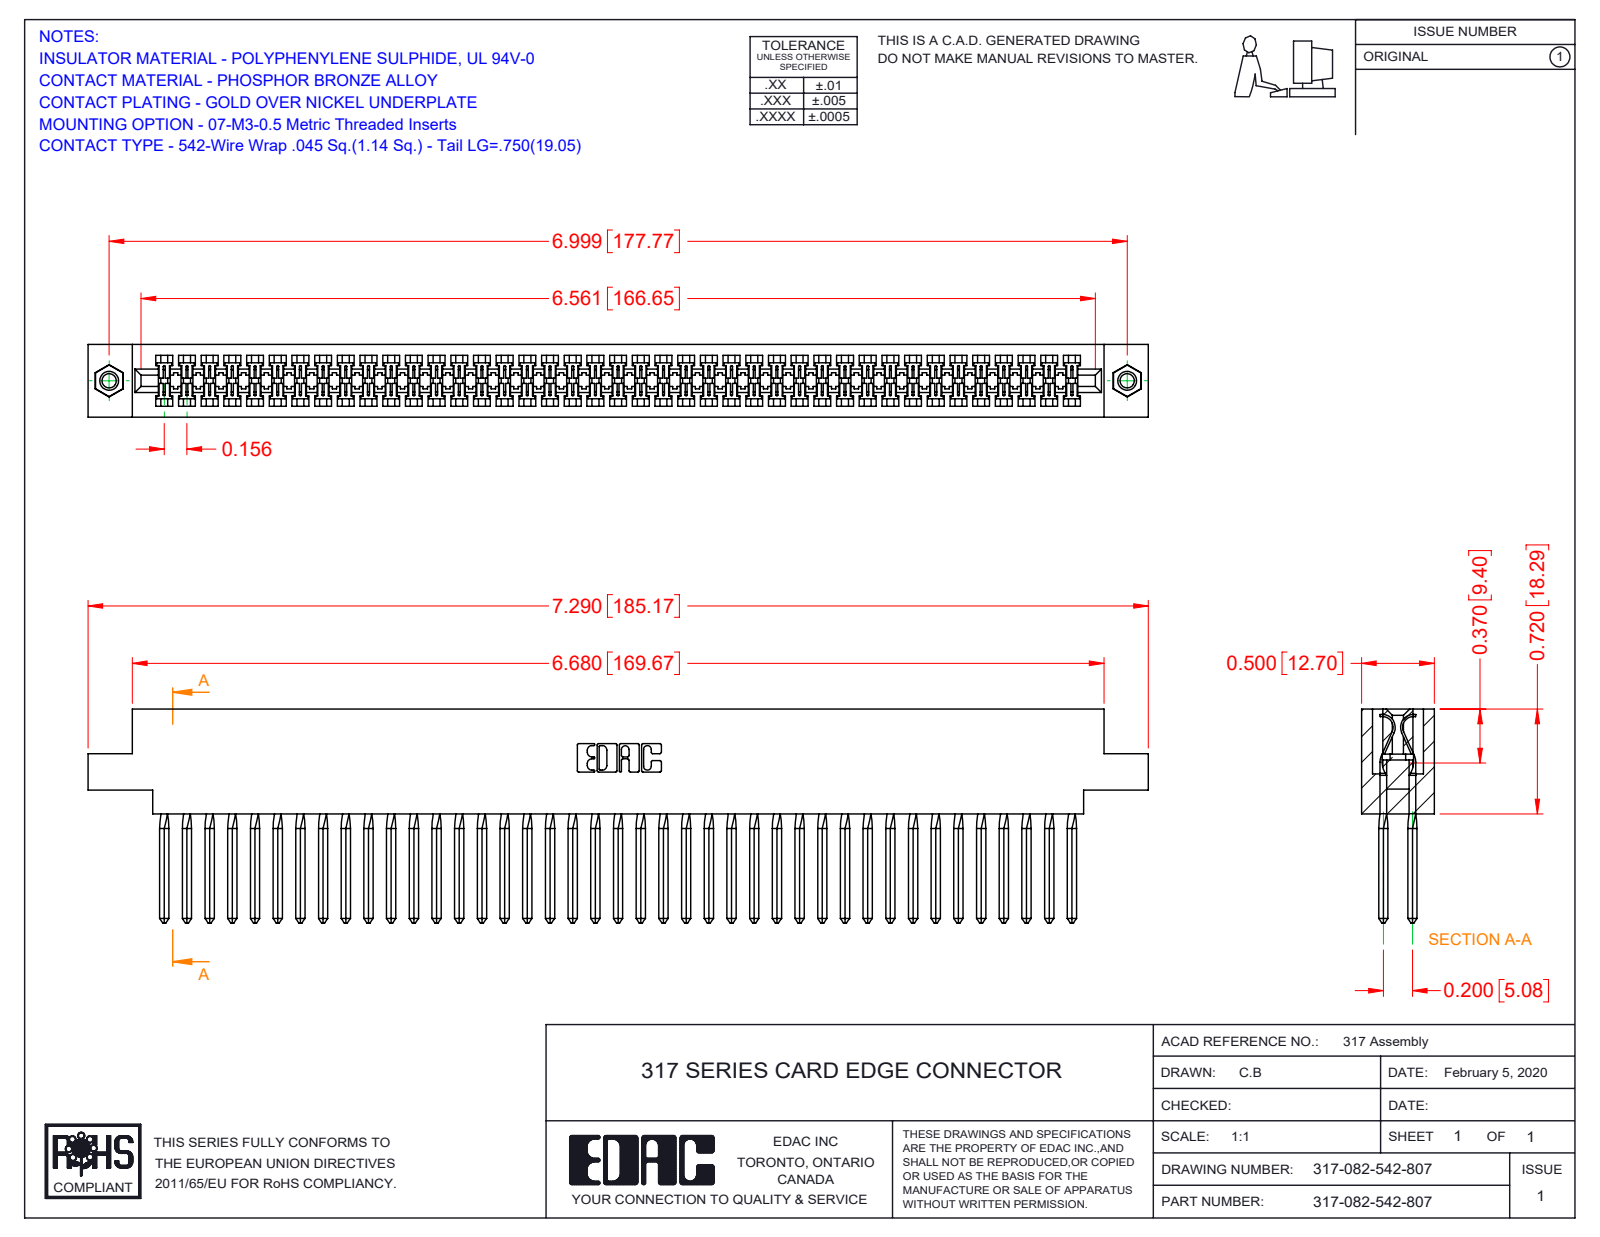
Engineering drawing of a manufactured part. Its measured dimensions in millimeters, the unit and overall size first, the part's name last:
Units: millimetres
Overall size (bounding box): 185.2 × 37.3 × 12.7
Round holes (diameter × count): ⌀2.5 ×2, ⌀3.2 ×2, ⌀4 ×2
Round bosses / shafts (diameter × count): ⌀3.9 ×2
Partial cylindrical surfaces — rounded edges, fillets, slot ends (radius × count): R0.2 ×164, R0.3 ×22, R0.2 ×6, R0.8 ×6, R0.7 ×3, R1.9 ×2, R2.3 ×2, R2.5 ×2
Main face-to-face distances: 12.7, 1.9, 10.8, 8.9, 5.1, 1.2, 3.3, 9.4, 1.3, 7.5
Hole centre spacings: 177.8
Volume: 30 280 mm³ · Surface area: 42 100 mm²
Bodies: 85 solids, 4836 faces (3862 planar, 630 cylindrical, 344 other)
Part name (STEP PRODUCT): 345-250-001_345-250-005-103; 317 Part_.156 Dia - TI; 317-290-003_542; 317-082-542-807
STEP written by: SolidWorks 2016 (CONFIG_CONTROL_DESIGN)
